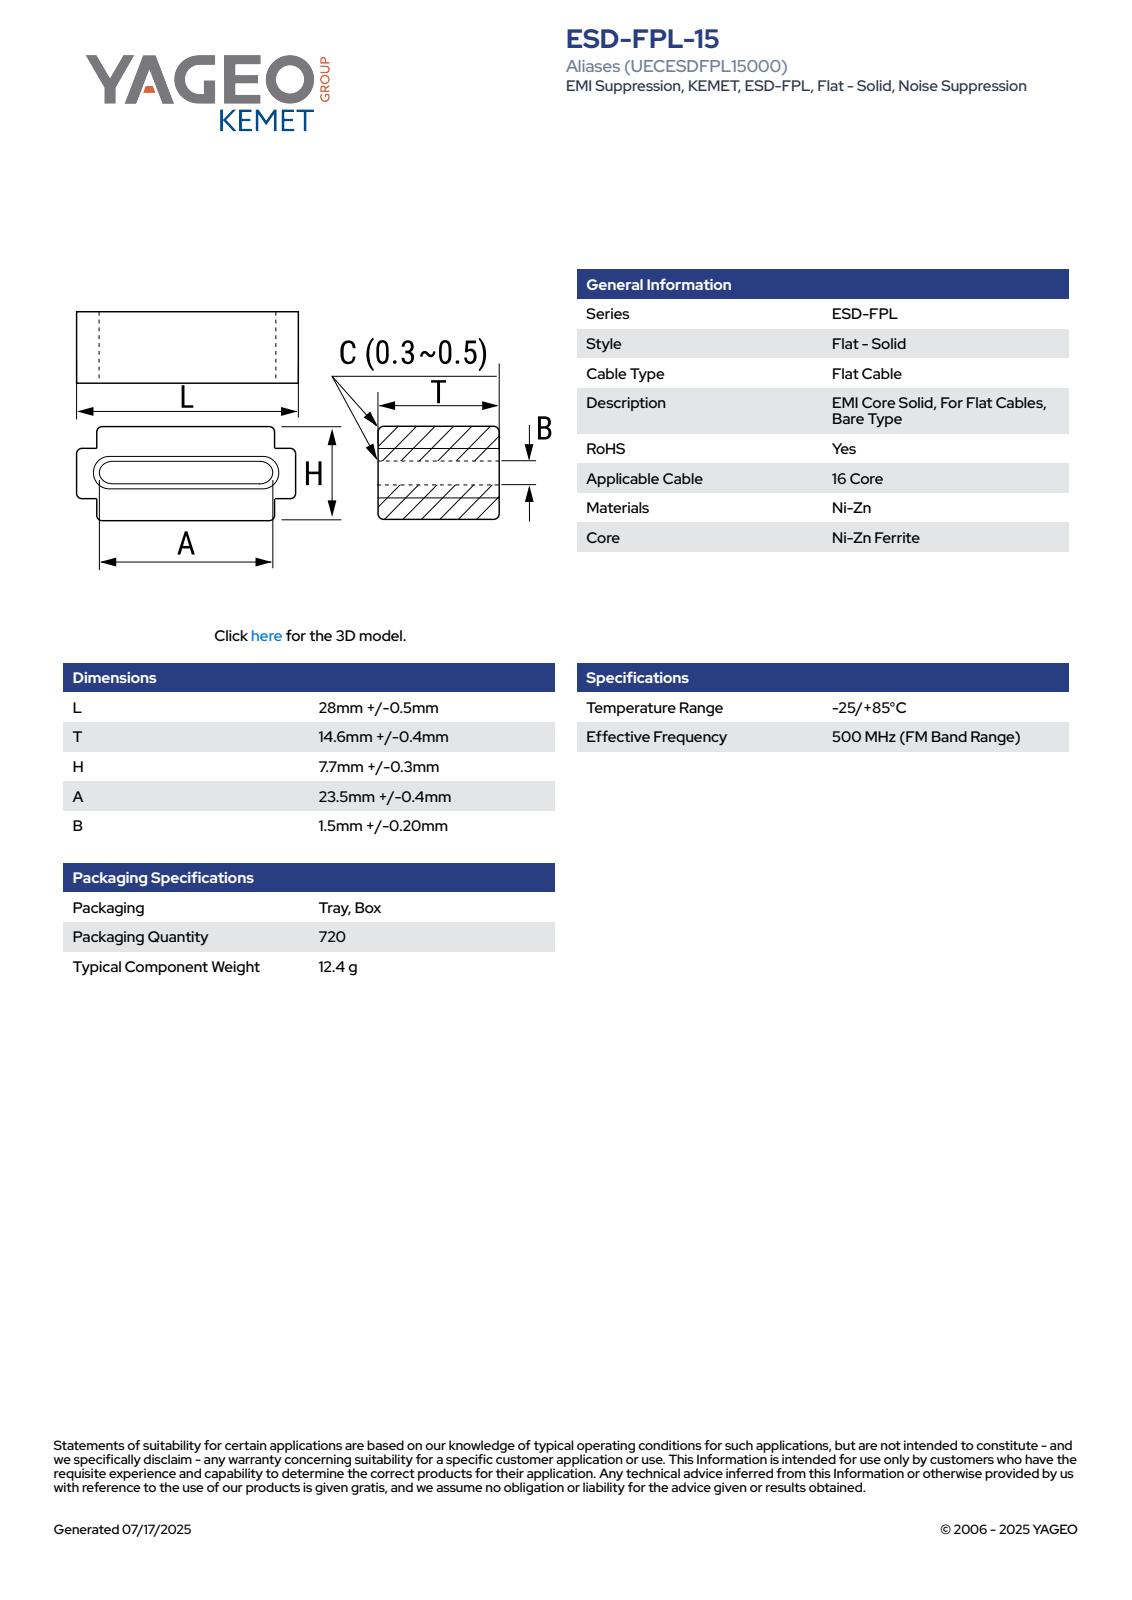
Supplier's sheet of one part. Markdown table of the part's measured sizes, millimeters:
| quantity | value |
| --- | --- |
| part name | EC_FPL2_L28.5T15H8A23.5B1.5 |
| STEP written by | SolidWorks 2014 (AUTOMOTIVE_DESIGN) |
| units | millimeters |
| bodies | 4 solids, 146 faces (73 planar, 43 cylindrical, 30 other) |
| overall size | 28 × 15 × 7.7 |
| volume | 2 419 mm³ |
| surface area | 2 109 mm² |
| partial cylindrical surfaces (radius × count) | 0.25 × 28, 0.15 × 4, 0.77 × 2 |
| main face-to-face distances | 3.1, 4.6, 7.7, 1.5, 2.2, 15, 5.5, 0.9, 2.4, 25.8 |
